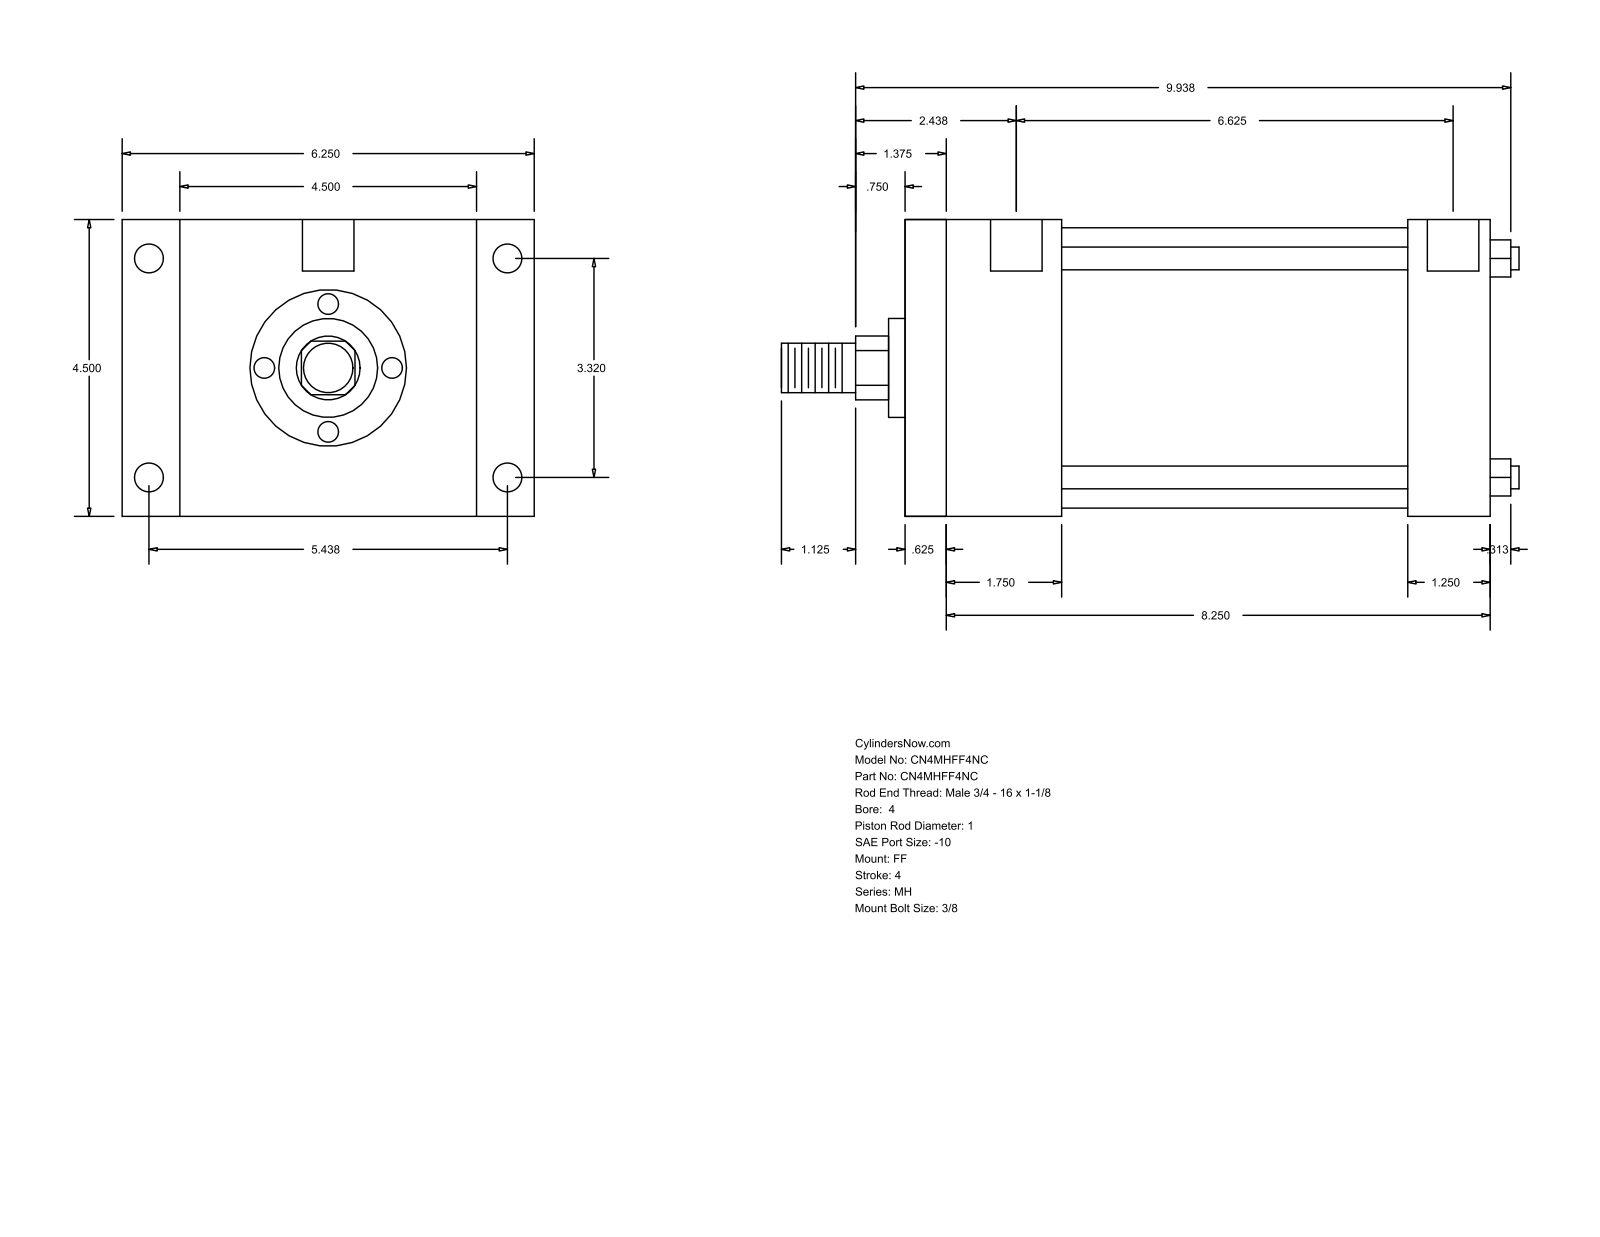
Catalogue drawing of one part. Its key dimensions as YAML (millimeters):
part_name: "MH_FF__0400_1"
step_written_by: "GSSL Pune (CONFIG_CONTROL_DESIGN)"
units: millimeters
bodies: {solids: 0, faces: 92, planar: 64, cylindrical: 28, other: 0}
overall_size: [284.16, 158.75, 114.3]
round_holes:
  - {diameter: 8.73, count: 4}
  - {diameter: 11.13, count: 4}
  - {diameter: 19.84, count: 2}
round_bosses_or_shafts:
  - {diameter: 8.76, count: 4}
  - {diameter: 107.95, count: 1}
  - {diameter: 38.1, count: 1}
  - {diameter: 25.4, count: 1}
  - {diameter: 19.05, count: 1}
partial_cylinders:
  - {radius: 12.29, count: 1}
face_to_face_distances: [114.3, 225.42, 15.87, 209.55, 60.33, 44.46, 165.09, 193.67, 177.8, 133.34]
hole_center_spacings: [84.32, 138.12, 161.82, 171.45, 1.58, 1.59, 168.28, 169.86]
